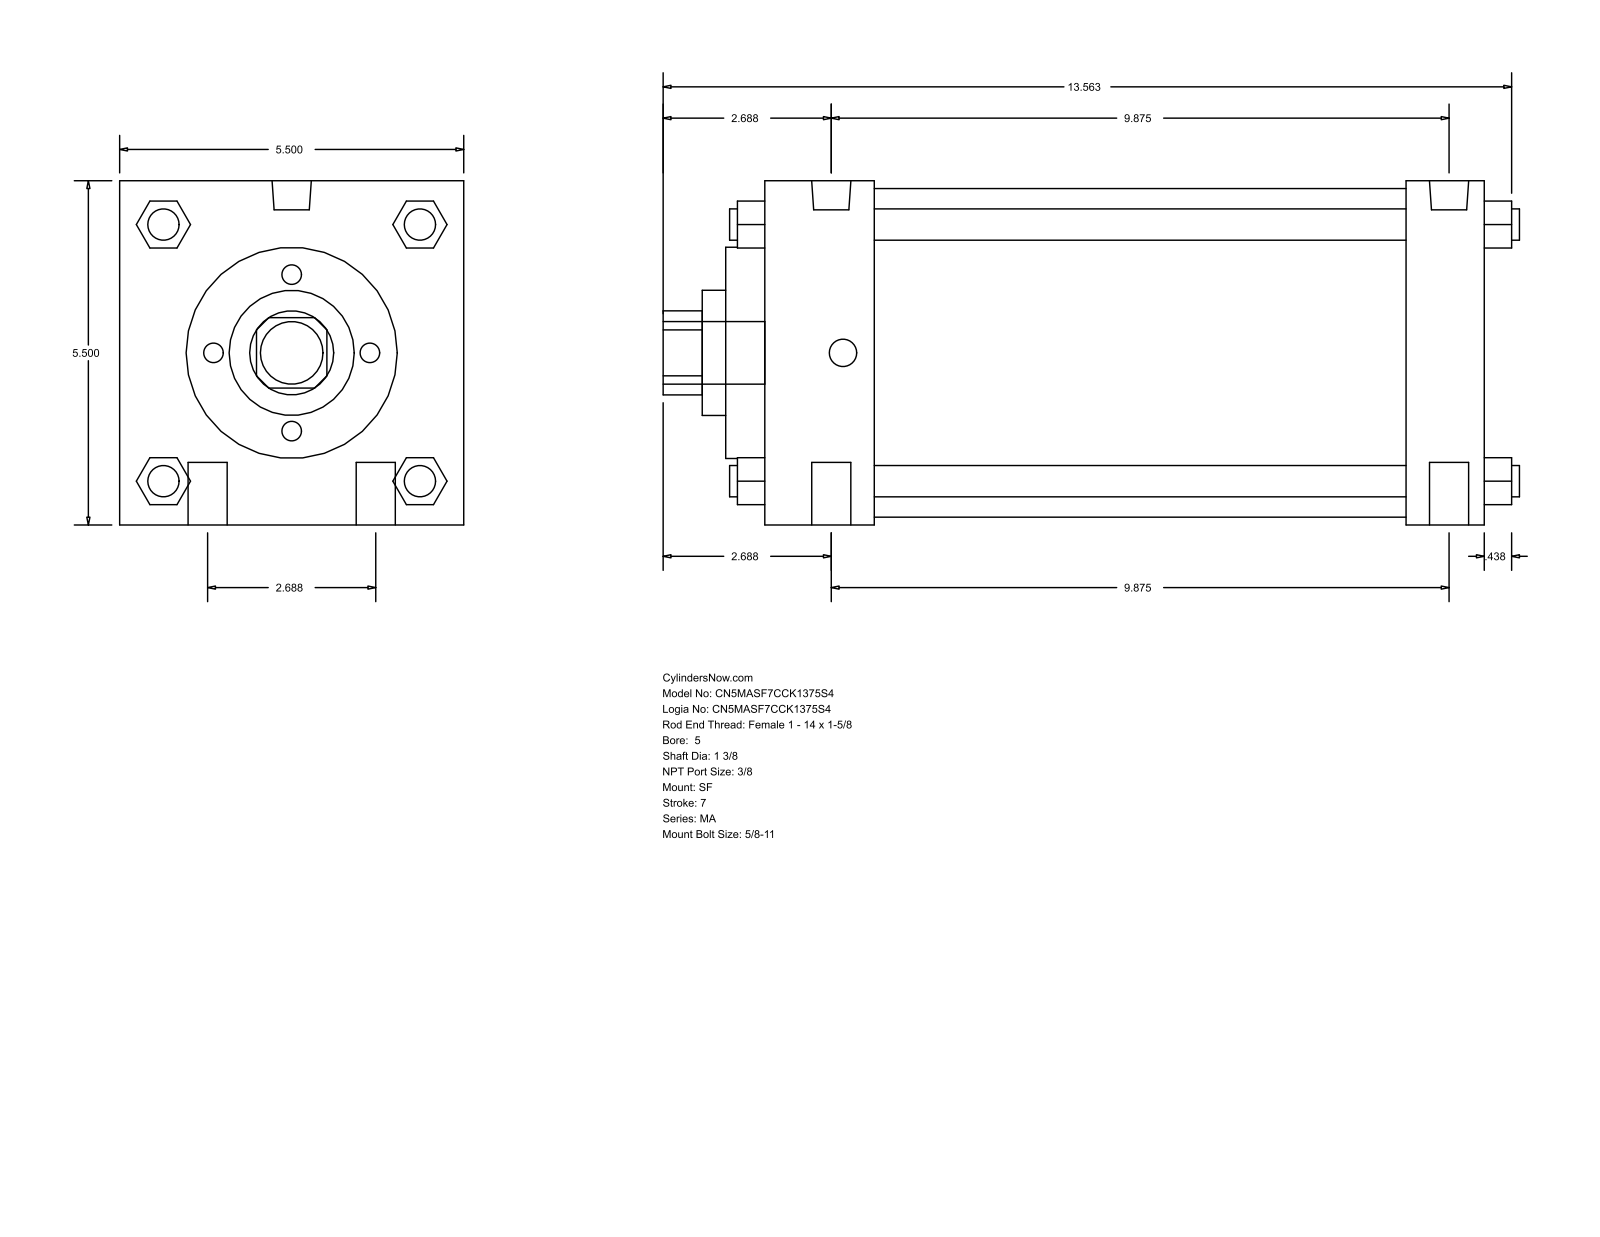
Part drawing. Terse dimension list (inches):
name: MA_SF__0500_1.375
written by: GSSL Pune (CONFIG_CONTROL_DESIGN)
unit: in
bodies: 0 solids, 126 faces (95 planar, 31 cylindrical, 0 other)
size: 13.687 × 5.5 × 5.5
holes: 1× ⌀1.375, 1× ⌀2, 1× ⌀3.375, 1× ⌀5.25
bosses: 4× ⌀0.625, 4× ⌀0.5, 2× ⌀0.627, 2× ⌀0.437, 1× ⌀1
rounds: 1× R0.672
face distances: 5.5, 11.5, 1.75, 10.25, 8.5, 9.75, 1.25, 0.625, 2.375, 10.875
